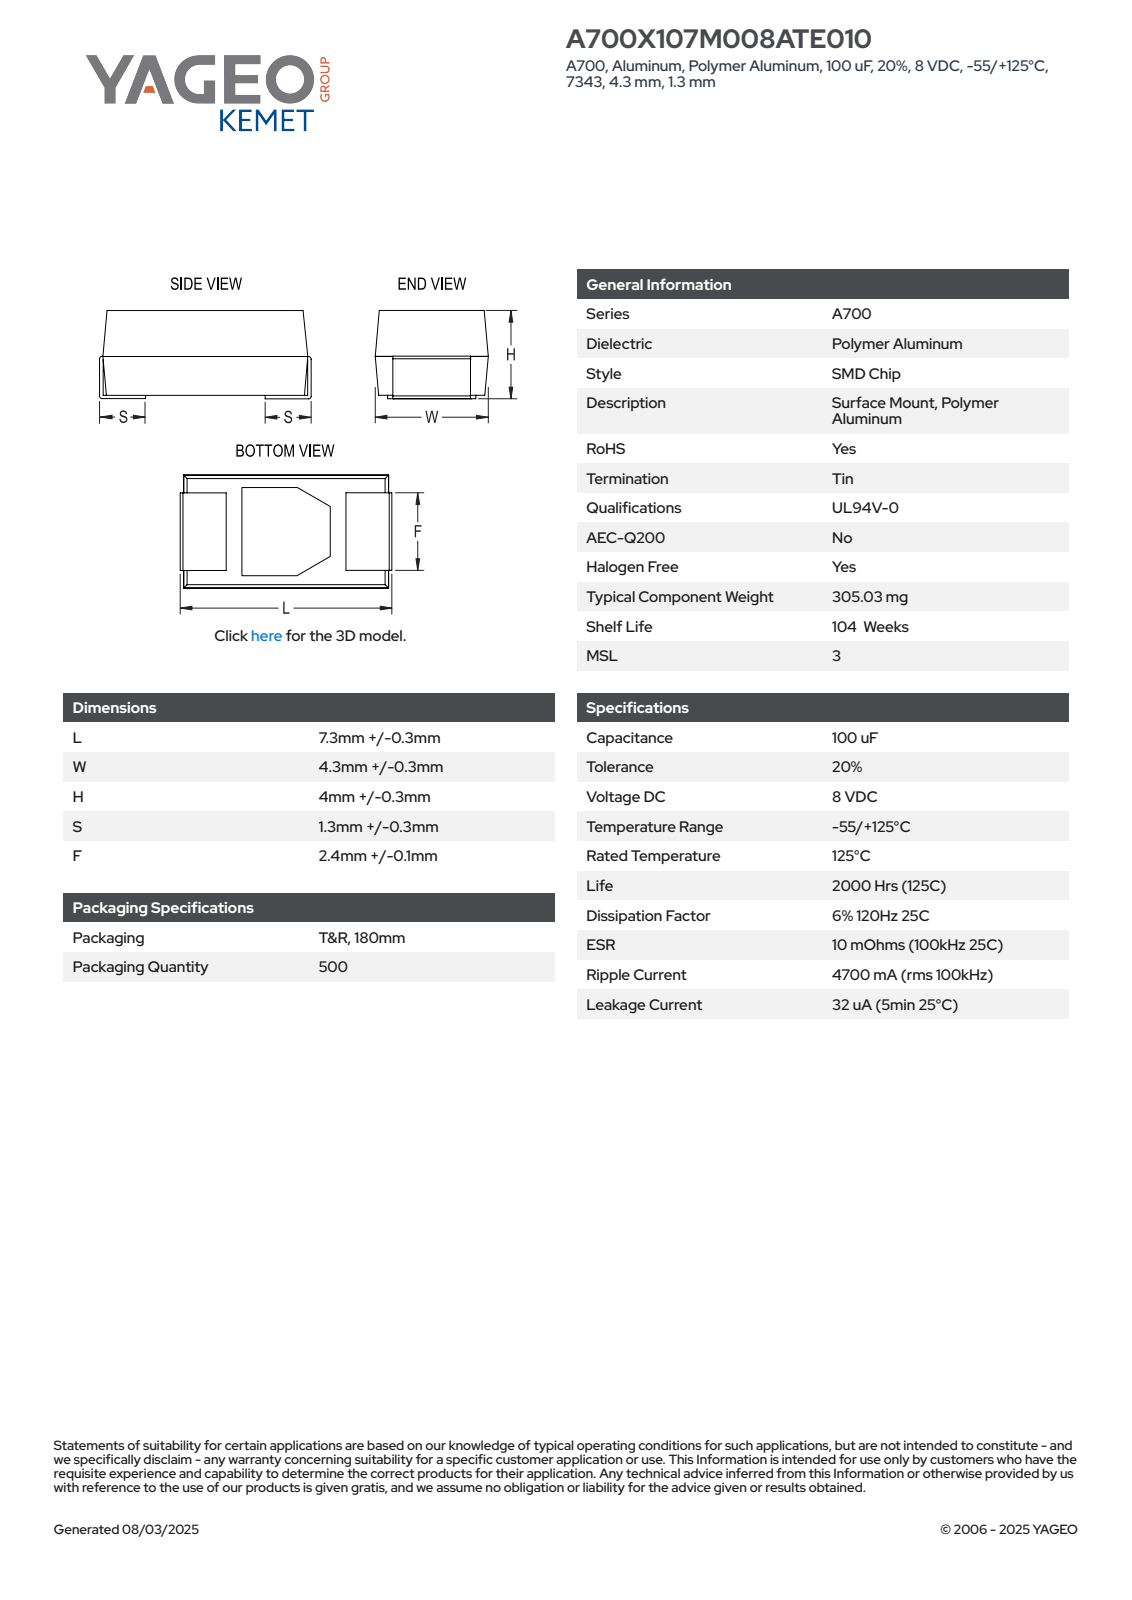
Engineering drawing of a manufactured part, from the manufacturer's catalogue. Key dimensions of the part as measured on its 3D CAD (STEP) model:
Part name (STEP PRODUCT): CAS_SMD_L7.6W4.6H4.3S1.3F2.5
STEP written by: SolidWorks 2021 (AUTOMOTIVE_DESIGN)
Units: millimetres
Bodies: 1 solid, 82 faces (78 planar, 4 cylindrical, 0 other)
Overall size (bounding box): 7.6 × 4.6 × 4.3
Volume: 134 mm³ · Surface area: 187 mm²
Partial cylindrical surfaces — rounded edges, fillets, slot ends (radius × count): R0.1 ×4
Main face-to-face distances: 4.58, 4.2, 7.35, 7.5, 4.3, 7.4, 7.6, 4.31, 4.21, 3
